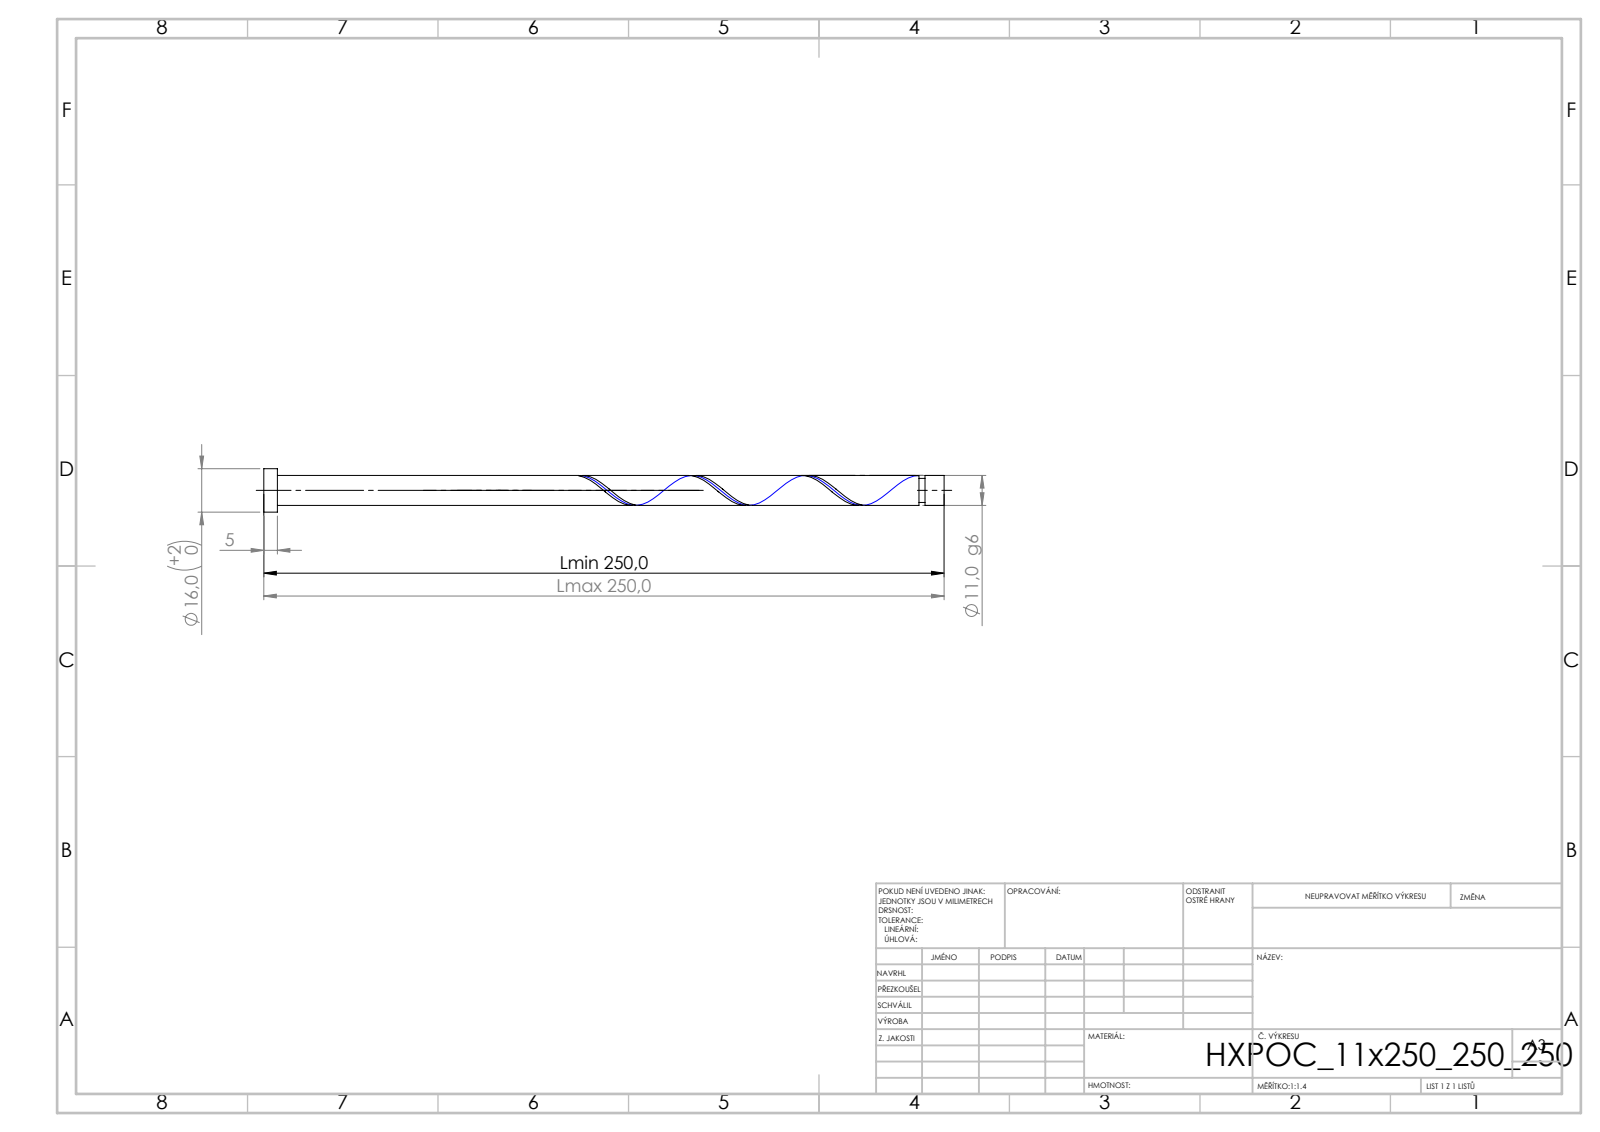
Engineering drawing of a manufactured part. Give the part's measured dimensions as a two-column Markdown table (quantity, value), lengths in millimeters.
| quantity | value |
| --- | --- |
| STEP written by | SolidWorks 2019 (CONFIG_CONTROL_DESIGN) |
| units | millimeters |
| bodies | 1 solid, 21 faces (6 planar, 14 cylindrical, 1 other) |
| overall size | 250 × 16 × 16 |
| volume | 23 986 mm³ |
| surface area | 9 361 mm² |
| round bosses / shafts (diameter × count) | 16 × 1, 11 × 1, 8.8 × 1 |
| main face-to-face distances | 5, 250, 245, 242.99, 237.99, 7.01, 240.79, 235.79, 2.2, 9.21 |
